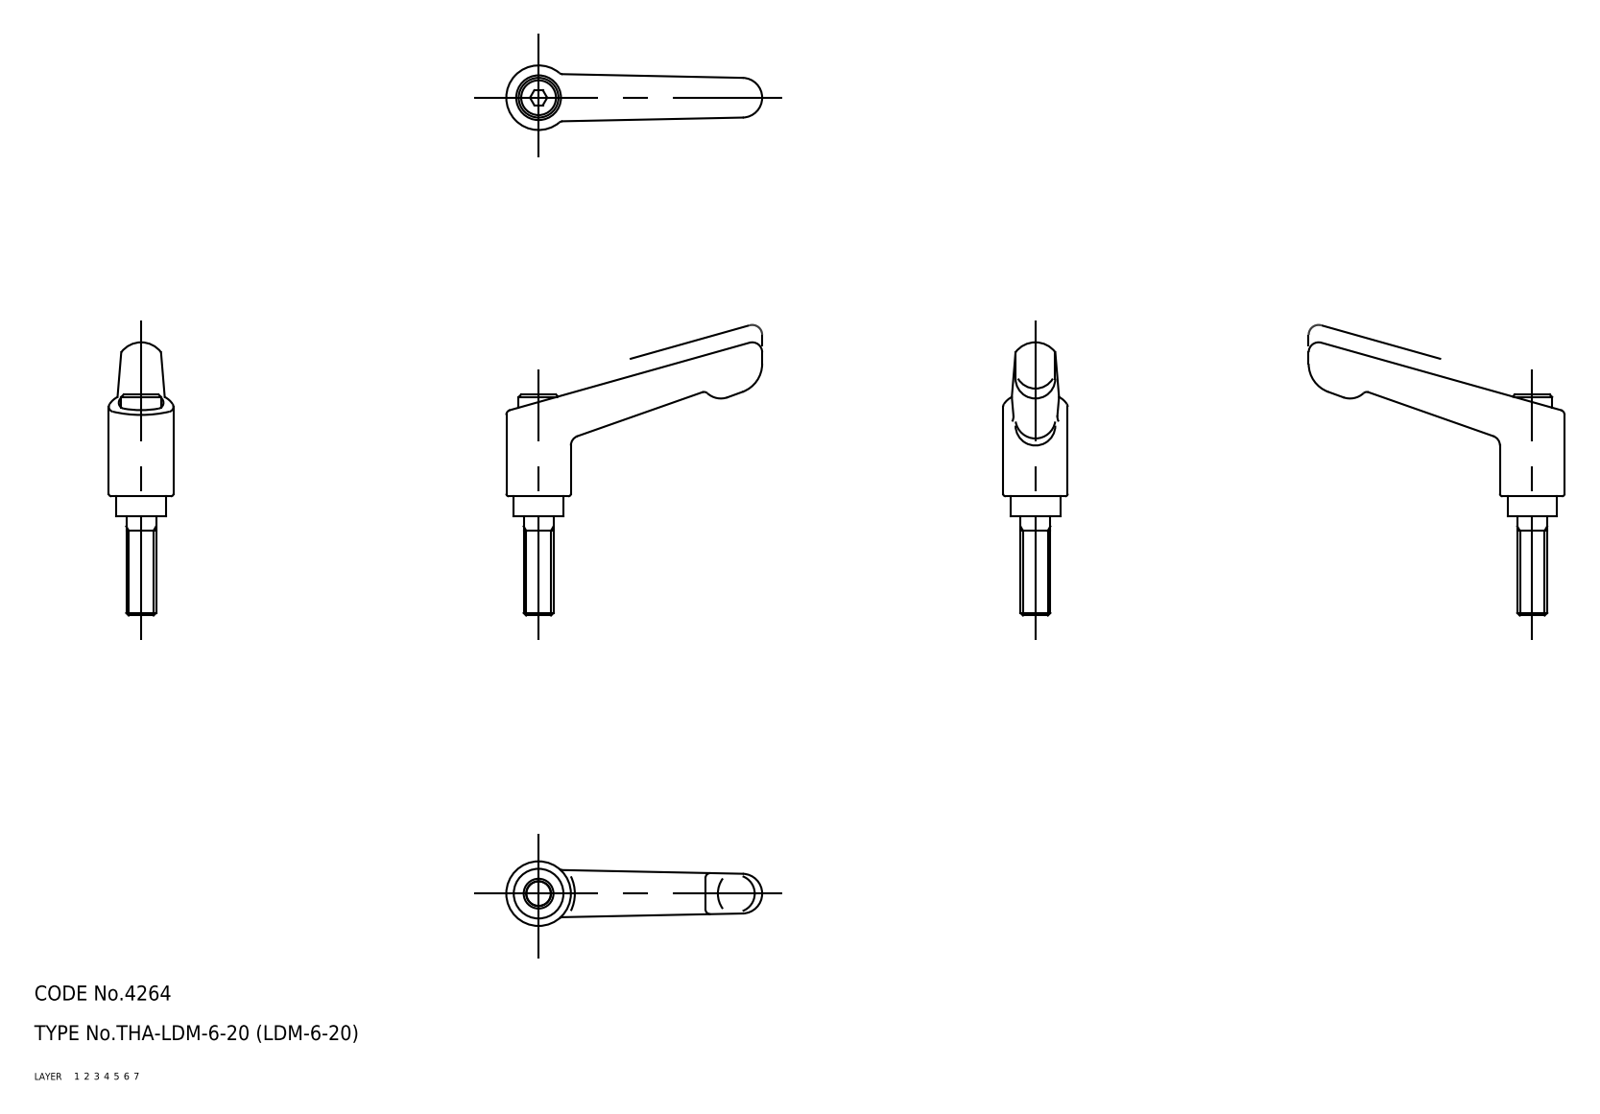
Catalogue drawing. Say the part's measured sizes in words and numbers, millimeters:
The part is named "sleeve; screw; handle; LDM_6_20_13146_36". Its 3-D file was written by "CADfix (AUTOMOTIVE_DESIGN)". It is 3 solids with 70 faces: 0 planar, 0 cylindrical and 70 other. Overall it measures 55 by 51.5 by 13 millimeters. Its volume is 5 695 cubic millimeters and its surface area 3 892 square millimeters.
